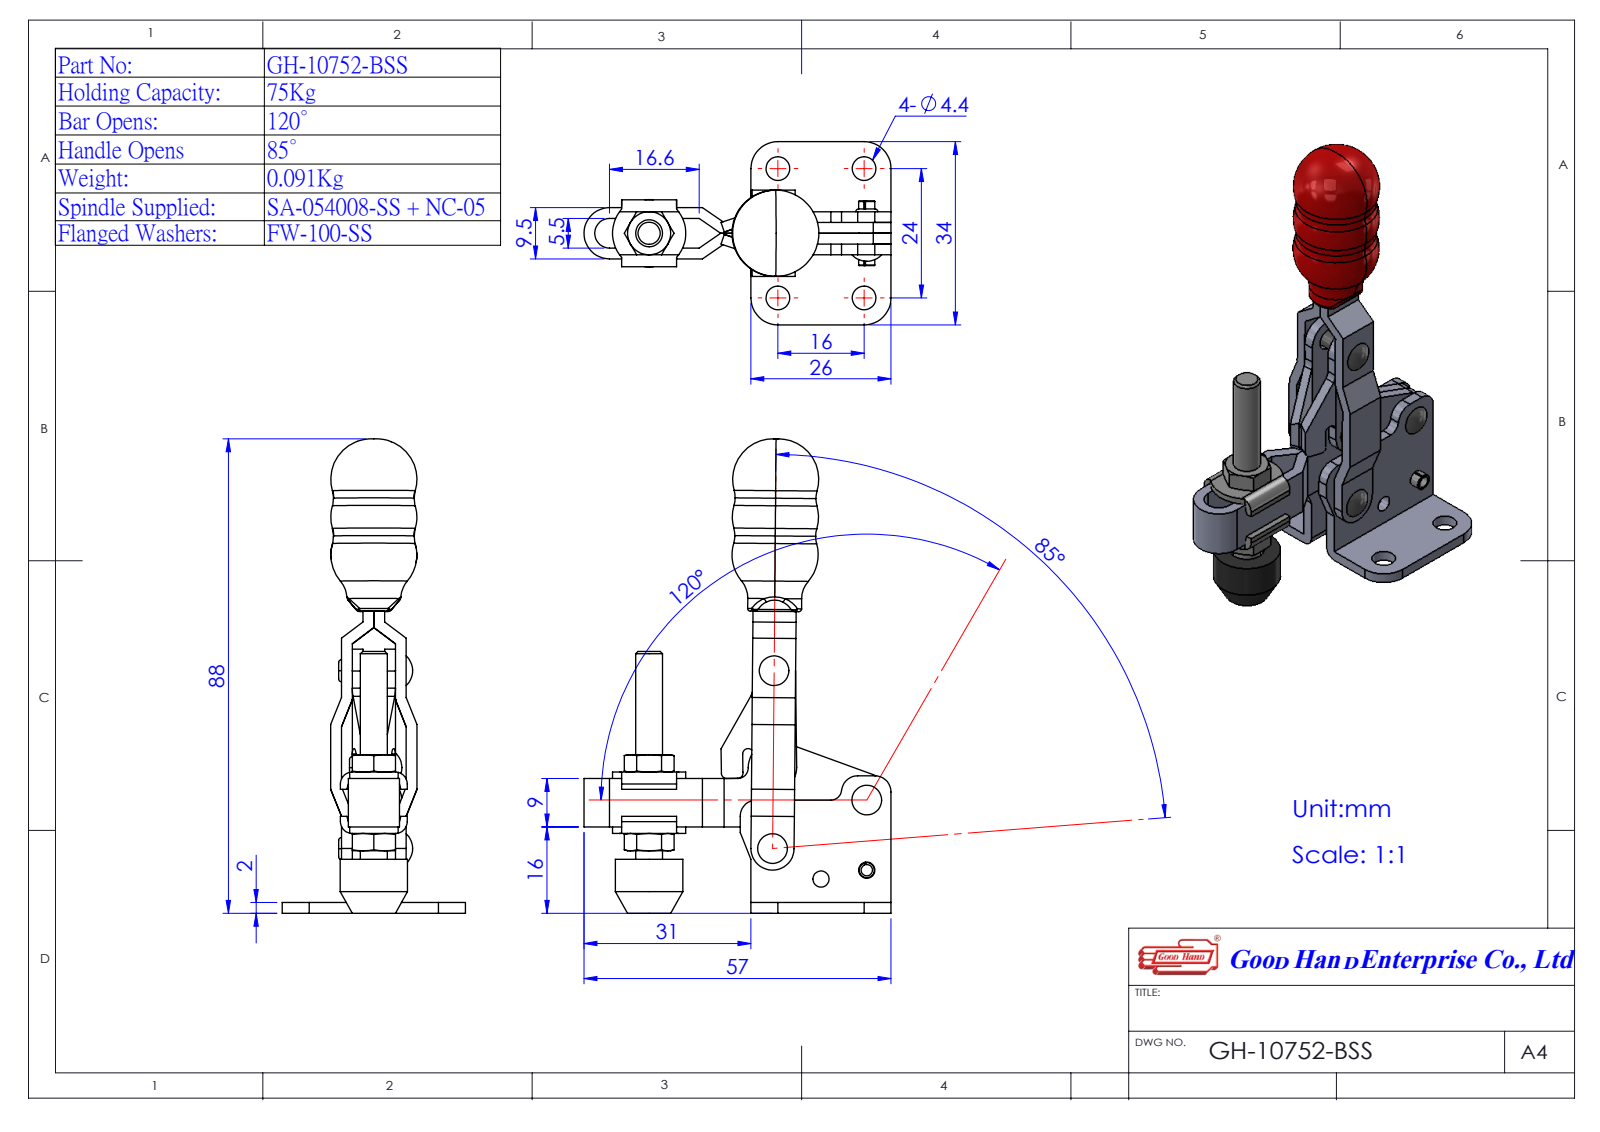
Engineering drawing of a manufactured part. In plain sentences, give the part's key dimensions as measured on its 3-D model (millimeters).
The part is named "Group1^493804(GH-10752-BSS); 110752B08-1^493804(GH-10752-BSS); 493804(GH-10752-BSS); Group2^493804(GH-10752-BSS) (+2 more)". Its 3-D file was written by "SolidWorks 2016 (AUTOMOTIVE_DESIGN)". It is 5 solids with 294 faces: 140 planar, 94 cylindrical and 60 other. Overall it measures 88.02 by 57 by 34 millimeters. Its volume is 16 264 cubic millimeters and its surface area 14 277 square millimeters. Round holes: 4 of diameter 3, 4 of diameter 4.4. Round bosses or shafts: 2 of diameter 4.1, 1 of diameter 12.5, 1 of diameter 10, 1 of diameter 5. Partial cylindrical surfaces (rounded edges, fillets, slot ends): 6 of radius 1, 6 of radius 5, 4 of radius 2.2, 4 of radius 3, 3 of radius 4, 2 of radius 2, 1 of radius 2.75, 1 of radius 4.75. The main face-to-face distances are 2, 4, 6, 8, 10, 1.25, 8.75, 0.75, 2.75, 4.75. The hole center spacings are 16, 24, 28.84, 15.01, 18, 18.03, 19.68, 29.53.
